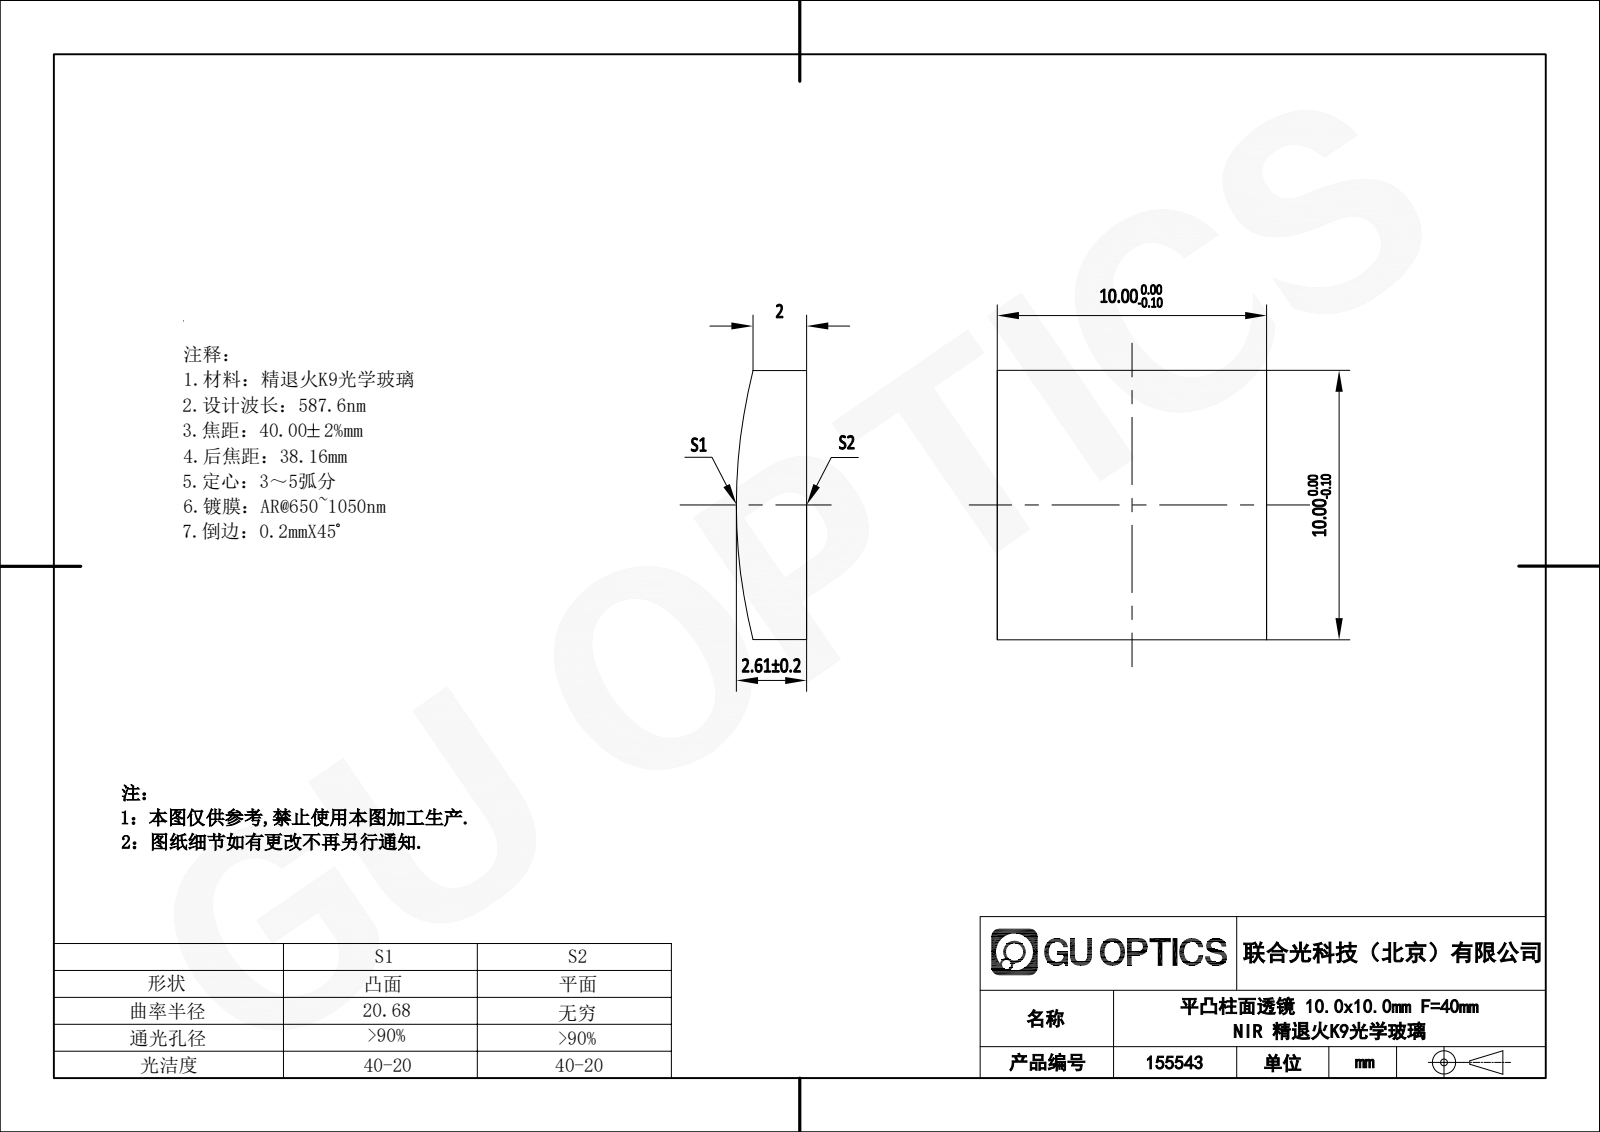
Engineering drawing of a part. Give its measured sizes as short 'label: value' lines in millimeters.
name: 155519
written by: SolidWorks 2020 (CONFIG_CONTROL_DESIGN)
unit: mm
bodies: 1 solid, 7 faces (5 planar, 2 cylindrical, 0 other)
size: 10 × 10 × 2.61
volume: 241 mm³; area: 289 mm²
rounds: 1× R20.68
face distances: 10
